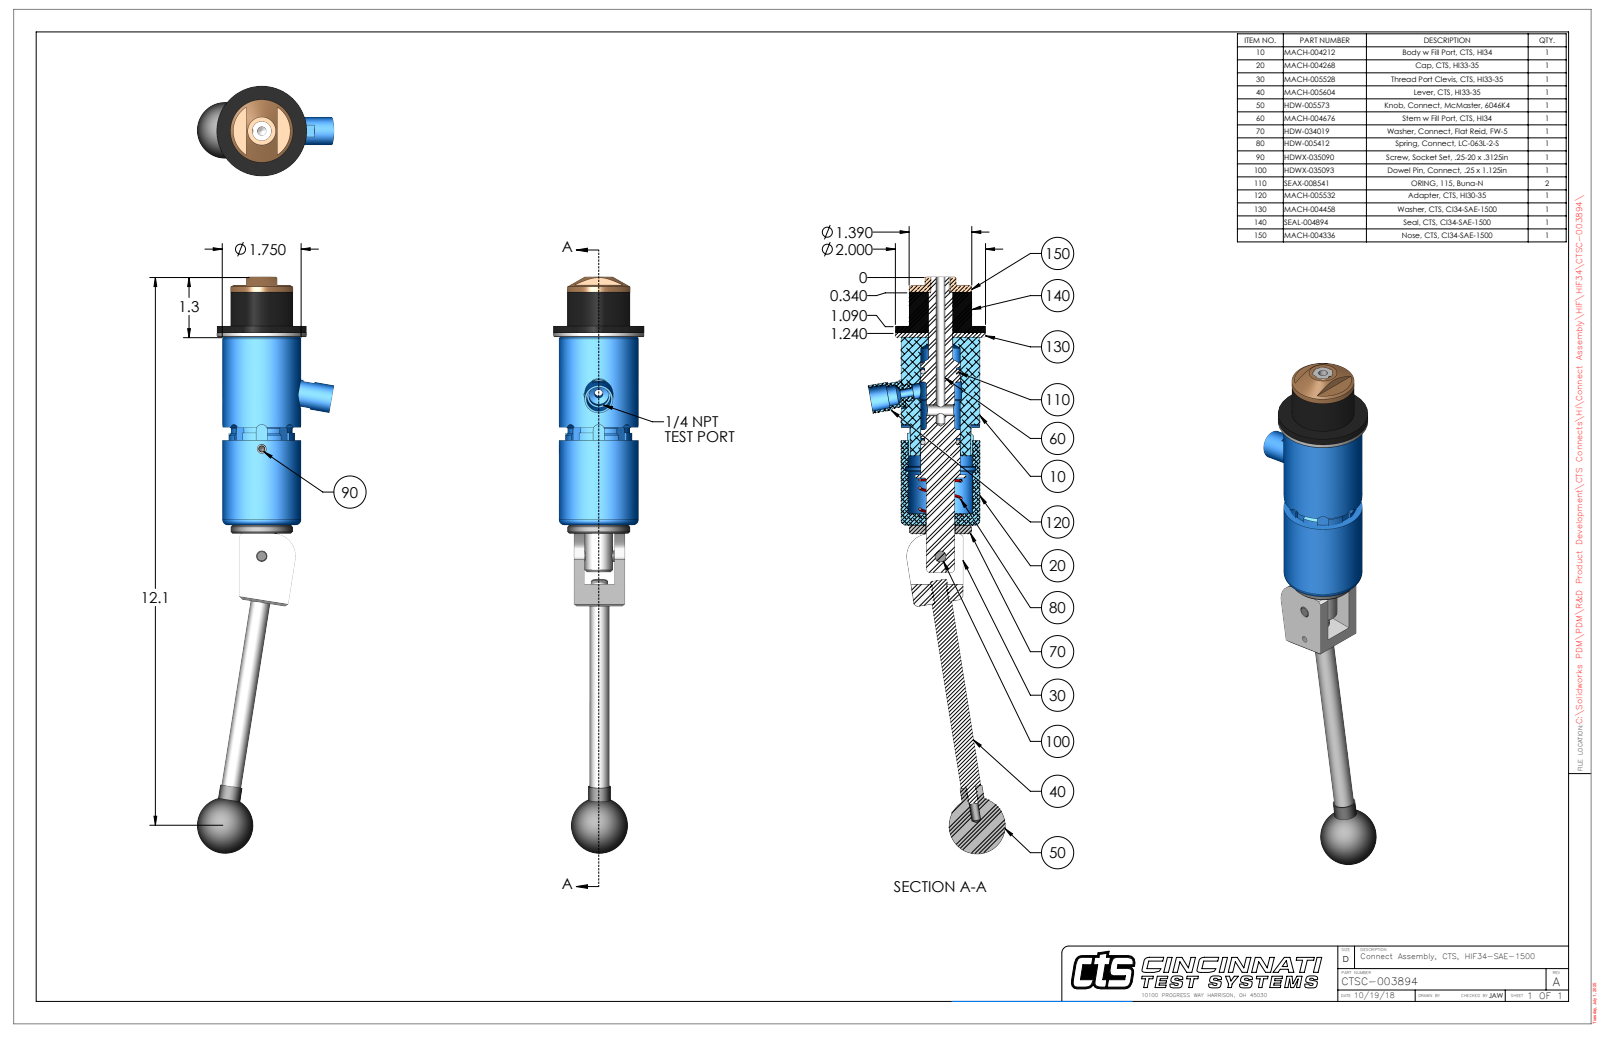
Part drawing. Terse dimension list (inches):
name: CTSC-003894
written by: SolidWorks 2023 (AUTOMOTIVE_DESIGN)
unit: in
bodies: 9 solids, 313 faces (114 planar, 135 cylindrical, 64 other)
size: 12.773 × 3.043 × 2
volume: 15.32 in³; area: 89.28 in²
holes: 2× ⌀0.201, 1× ⌀0.15, 1× ⌀0.187, 1× ⌀0.204, 1× ⌀0.249, 1× ⌀0.25, 1× ⌀0.251, 1× ⌀0.313, 1× ⌀0.422, 1× ⌀0.438, 1× ⌀0.53, 1× ⌀0.541
bosses: 2× ⌀0.5, 2× ⌀0.44, 2× ⌀0.25, 1× ⌀2, 1× ⌀1.75, 1× ⌀1.39, 1× ⌀1.38, 1× ⌀0.625
rounds: 4× R0.125, 2× R0.029, 1× R0.166, 1× R0.166, 1× R0.184, 1× R0.33, 1× R0.5, 1× R0.709
face distances: 0.094, 0.9, 0.994, 5.158, 4.258, 4.164, 1.12, 0.75, 0.15, 0.244
hole spacings: 0.74, 2.376, 3.116
